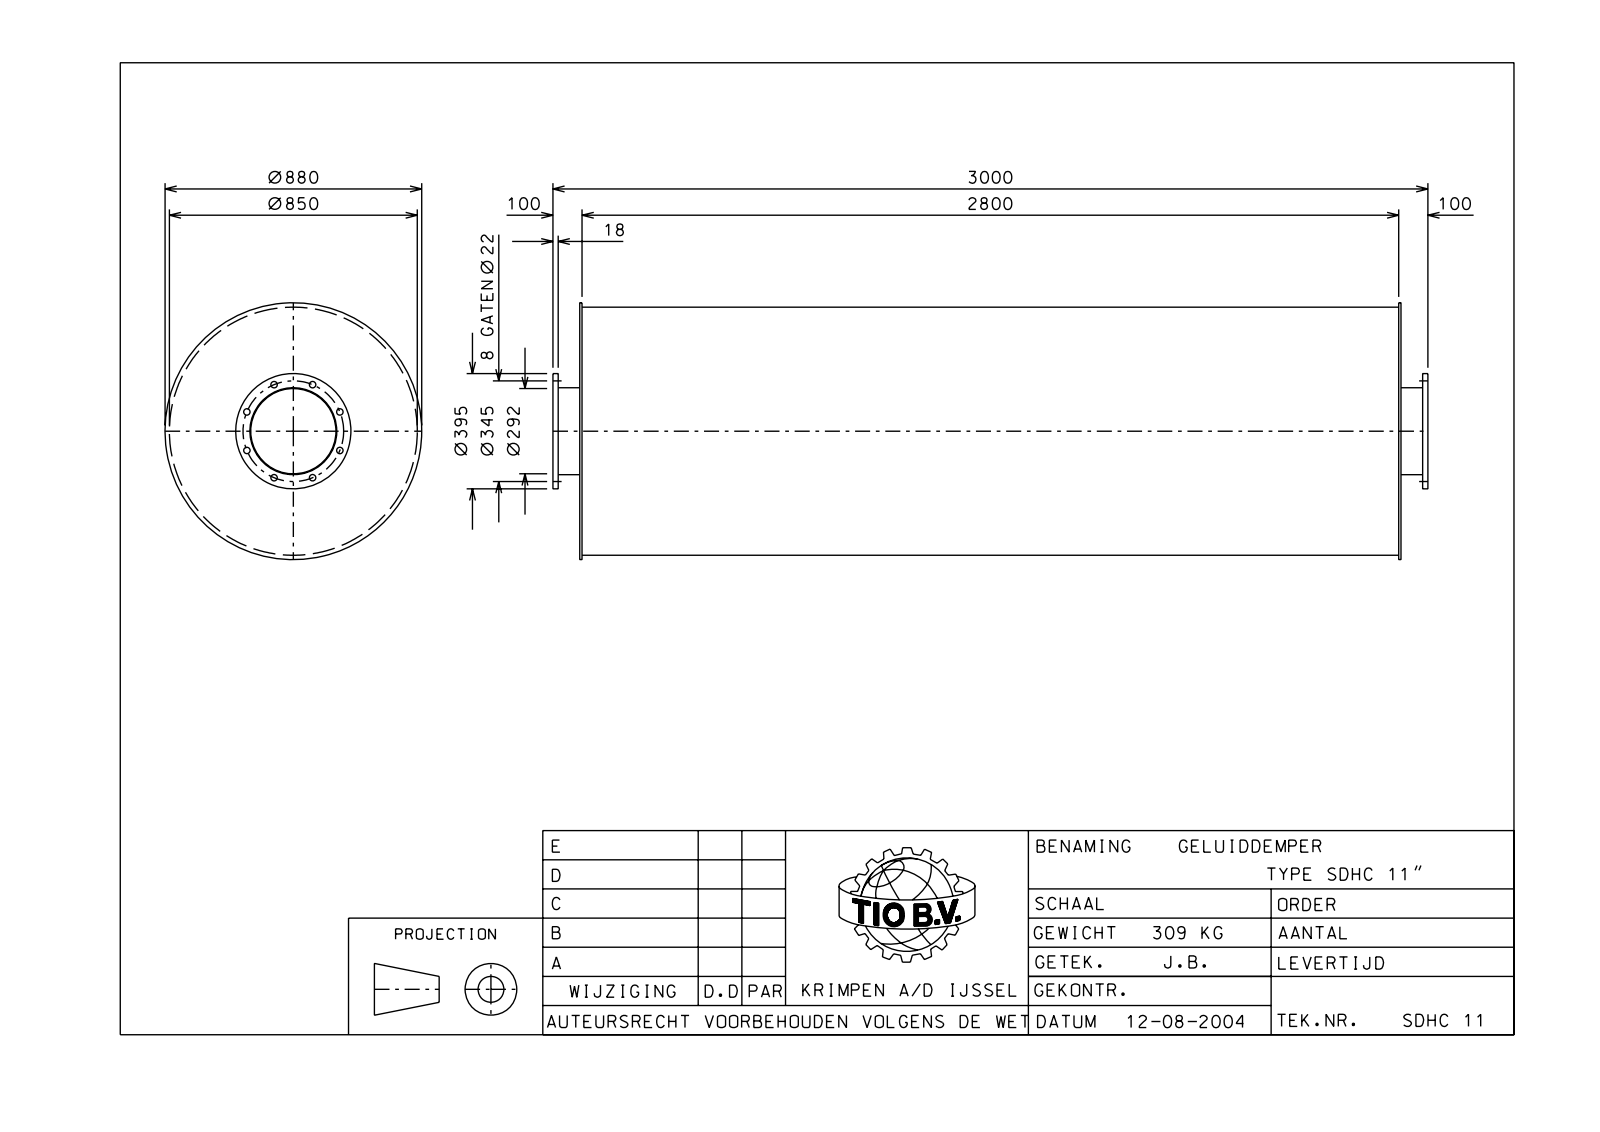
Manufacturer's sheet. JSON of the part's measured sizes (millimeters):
{"part_name": "MAAT3D", "step_written_by": "Autodesk Inventor 2015 (AUTOMOTIVE_DESIGN)", "units": "millimeters", "bodies": {"solids": 8, "faces": 48, "planar": 16, "cylindrical": 32, "other": 0}, "overall_size": [3000, 880, 880], "volume_mm3": 33240000, "surface_area_mm2": 17800000, "round_holes": [[22, 8], [292, 1], [300, 1], [844, 1]], "round_bosses_or_shafts": [[880, 1], [850, 1], [395, 1], [298, 1]], "face_to_face_distances": [8, 2808, 2800, 2816, 92, 100, 2900, 2908, 2982, 74], "hole_center_spacings": [172.5, 243.95, 318.74, 132.02, 132.03, 345]}
